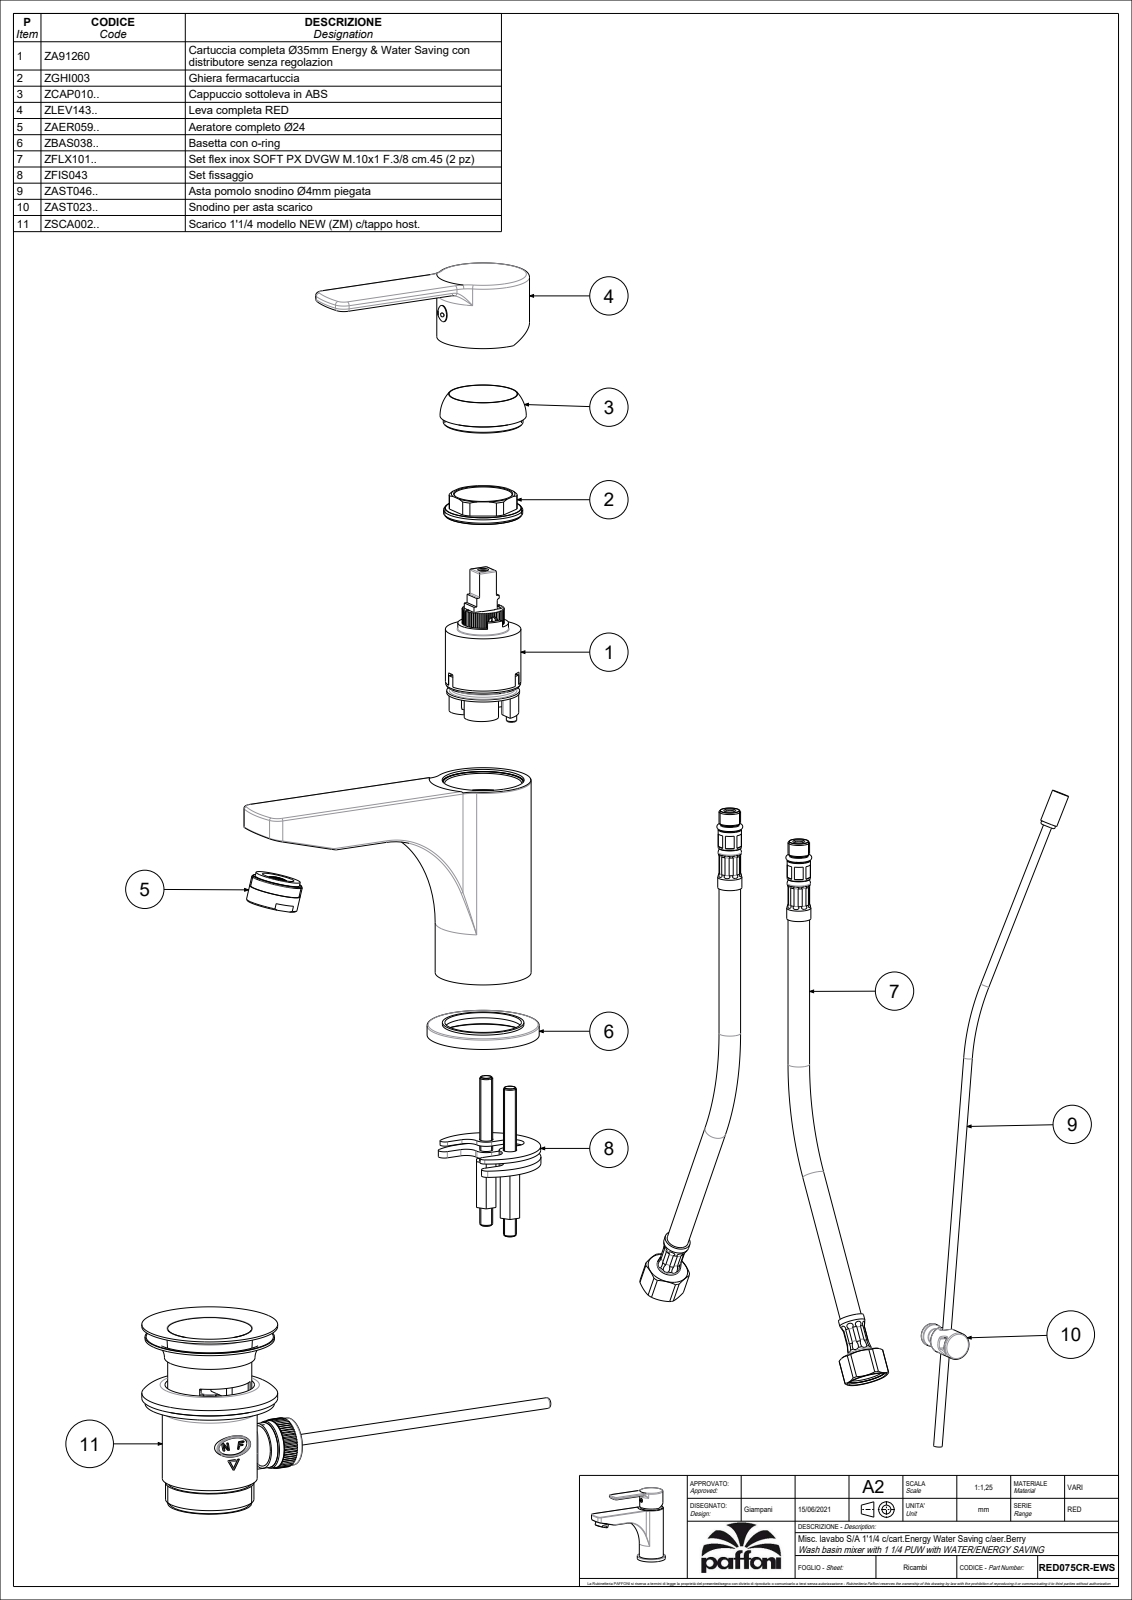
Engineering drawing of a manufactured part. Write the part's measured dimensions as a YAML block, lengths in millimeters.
part_name: "RED075CR"
step_written_by: "CREO PARAMETRIC BY PTC INC, 2020044 (CONFIG_CONTROL_DESIGN)"
units: millimeters
bodies: {solids: 6, faces: 3092, planar: 2173, cylindrical: 531, other: 388}
overall_size: [160.35, 130.73, 52]
volume: 148360
surface_area: 97566
round_holes:
  - {diameter: 9, count: 5}
  - {diameter: 5, count: 4}
  - {diameter: 4.5, count: 3}
  - {diameter: 12, count: 3}
  - {diameter: 3.3, count: 2}
  - {diameter: 4, count: 2}
  - {diameter: 5.5, count: 2}
  - {diameter: 6, count: 2}
  - {diameter: 6.5, count: 2}
  - {diameter: 8, count: 2}
  - {diameter: 3, count: 1}
  - {diameter: 3.5, count: 1}
round_bosses_or_shafts:
  - {diameter: 11.2, count: 2}
  - {diameter: 10.8, count: 2}
  - {diameter: 10, count: 2}
  - {diameter: 8.2, count: 2}
  - {diameter: 6, count: 2}
  - {diameter: 4.8, count: 2}
  - {diameter: 52, count: 1}
  - {diameter: 44.5, count: 1}
partial_cylinders:
  - {radius: 0.5, count: 88}
  - {radius: 1, count: 26}
  - {radius: 1.26, count: 14}
  - {radius: 2.05, count: 14}
  - {radius: 0.15, count: 11}
  - {radius: 0.3, count: 9}
  - {radius: 1.5, count: 4}
  - {radius: 5, count: 4}
face_to_face_distances: [3.5, 27.5, 31.5, 28, 31, 32.5, 4.5, 15.5, 36, 24]
hole_center_spacings: [13.6, 0.71, 2.83, 8.51, 8.6, 9.66, 9.85, 11.18]
